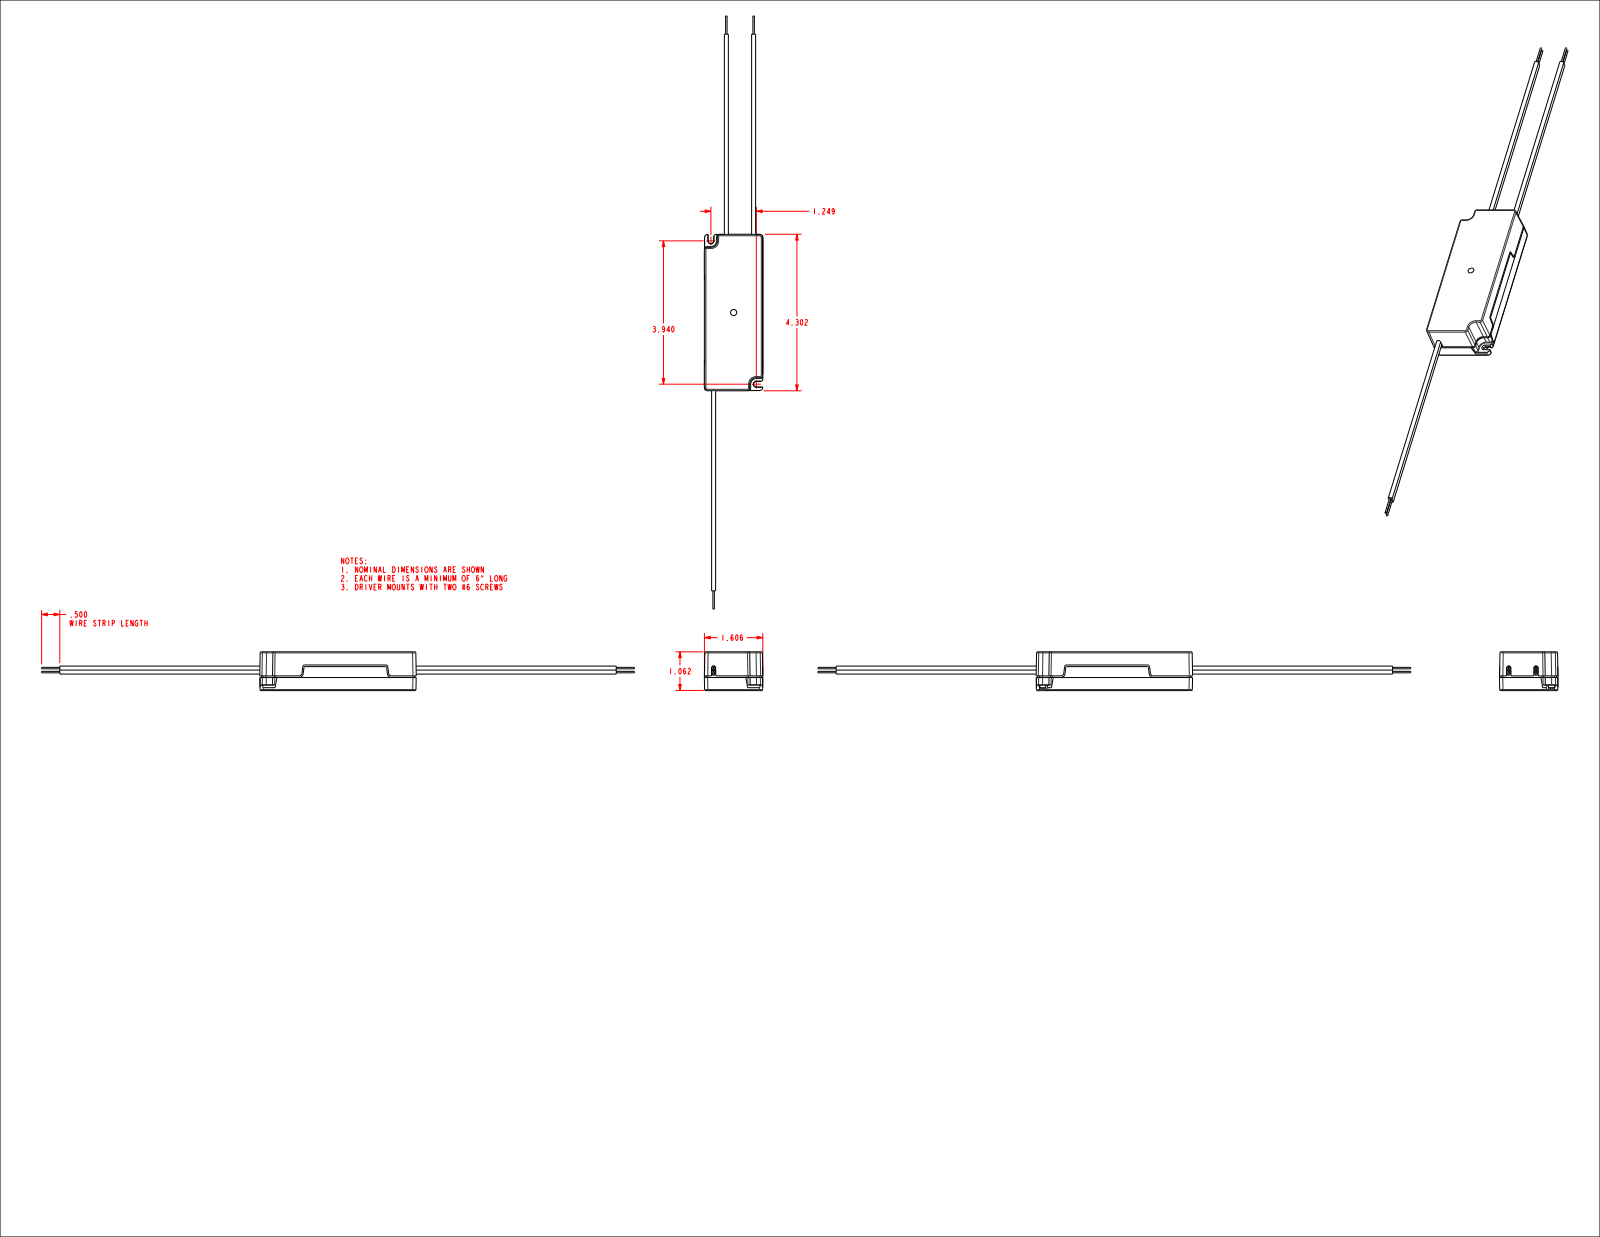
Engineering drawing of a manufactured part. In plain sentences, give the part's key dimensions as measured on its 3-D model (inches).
The part is named "2442190; 2442191; GRY_WIRE; WIRES_ASM (+1 more)". Its 3-D file was written by "CREO PARAMETRIC BY PTC INC, 2017380 (CONFIG_CONTROL_DESIGN)". It is 8 solids with 880 faces: 285 planar, 340 cylindrical and 255 other. Overall it measures 16.302 by 1.609 by 1.066 inches. Its volume is 2.234 cubic inches and its surface area 64.73 square inches. Round bosses or shafts: 6 of diameter 0.11, 6 of diameter 0.04. Partial cylindrical surfaces (rounded edges, fillets, slot ends): 58 of radius 0.018, 54 of radius 0.004, 42 of radius 0.005, 26 of radius 0.015, 12 of radius 0.03, 9 of radius 0.02, 8 of radius 0.06, 6 of radius 0.008. The main face-to-face distances are 0.084, 0.982, 1.066, 0.898, 1.608, 0.048, 1.481, 1.474, 1.609, 0.042.
